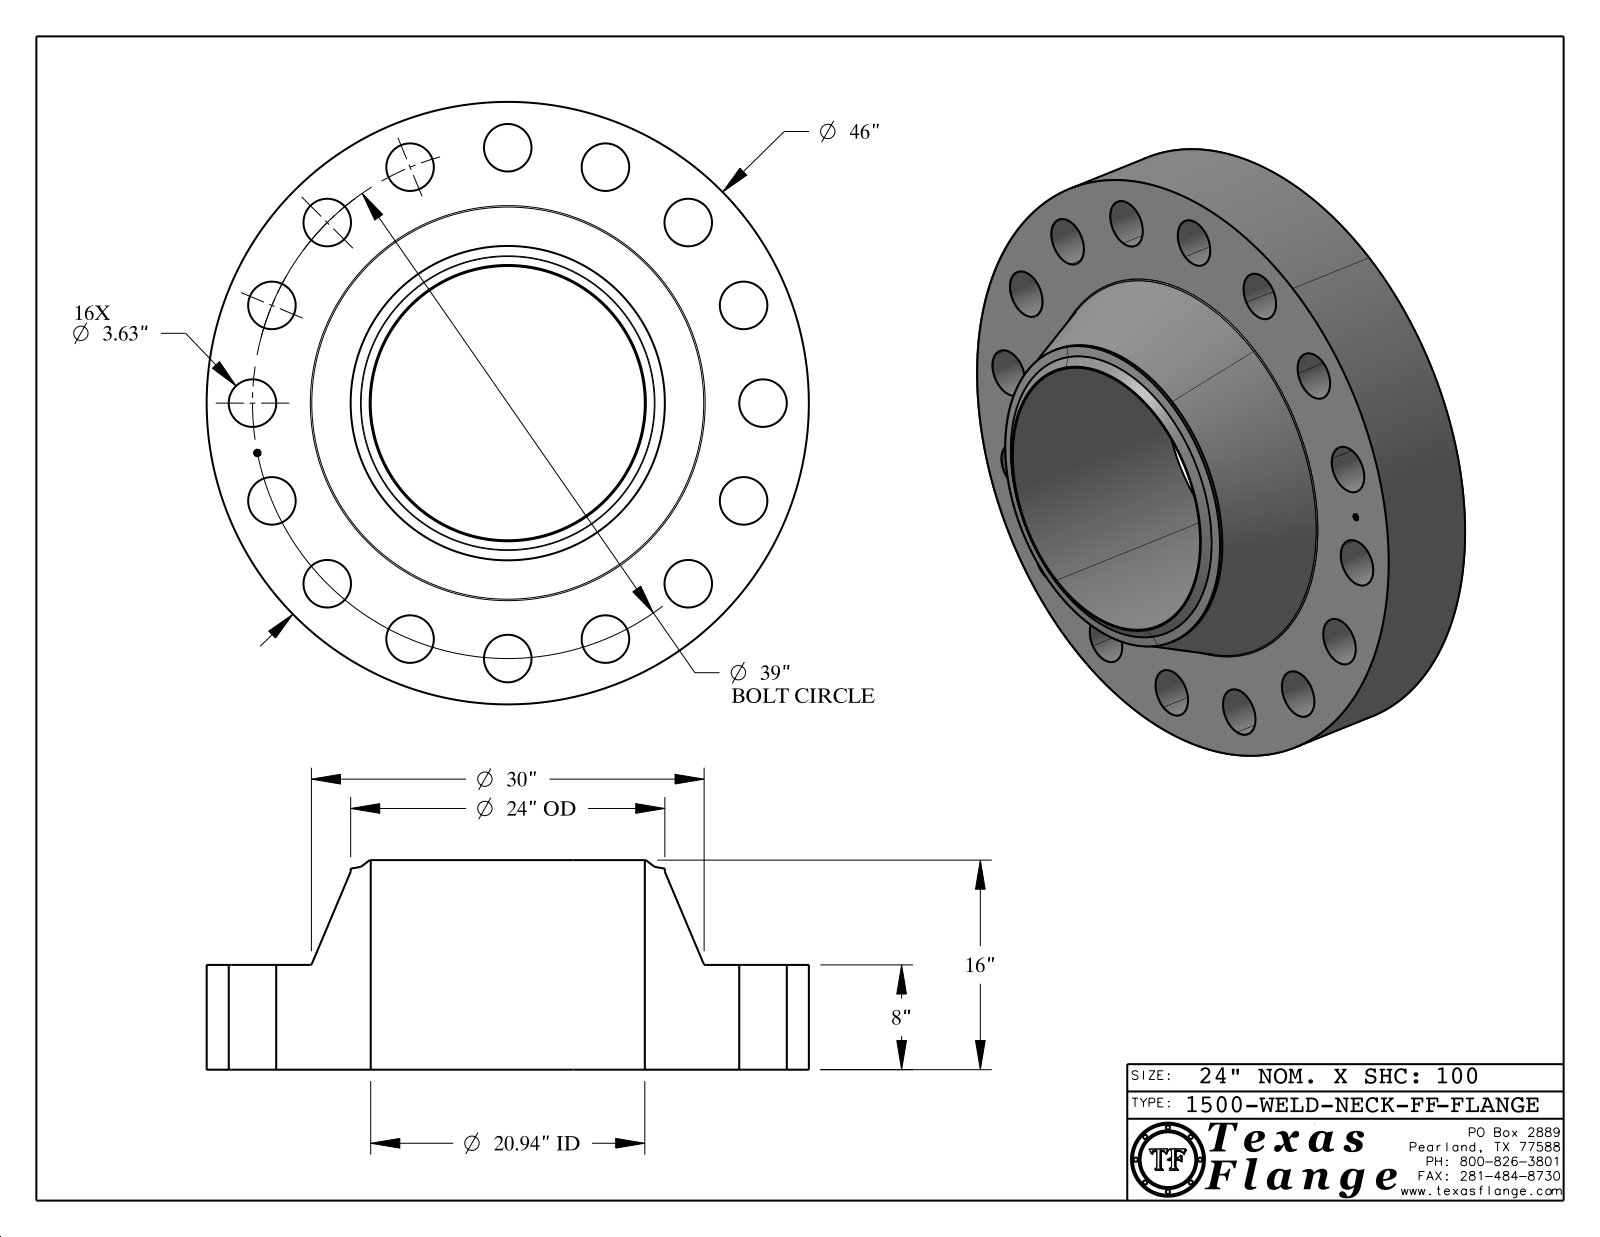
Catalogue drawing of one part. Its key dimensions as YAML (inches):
part_name: "1500-WELD-NECK-FF"
step_written_by: "CATIA V5 STEP AP214 (AUTOMOTIVE_DESIGN)"
units: inches
bodies: {solids: 1, faces: 436, planar: 368, cylindrical: 58, other: 10}
overall_size: [46, 46, 16]
volume: 10907
surface_area: 6401
round_holes:
  - {diameter: 3.63, count: 16}
  - {diameter: 0.495, count: 1}
  - {diameter: 20.938, count: 1}
round_bosses_or_shafts:
  - {diameter: 0.03, count: 8}
  - {diameter: 46, count: 1}
  - {diameter: 24, count: 1}
  - {diameter: 0.39, count: 1}
face_to_face_distances: [8, 16, 7.985, 0.015, 8.015, 0.148, 0.145, 0.027, 0.096, 0.123]
hole_center_spacings: [19.5, 21.667, 27.577, 38.251, 14.925, 36.031, 7.608, 7.609]
